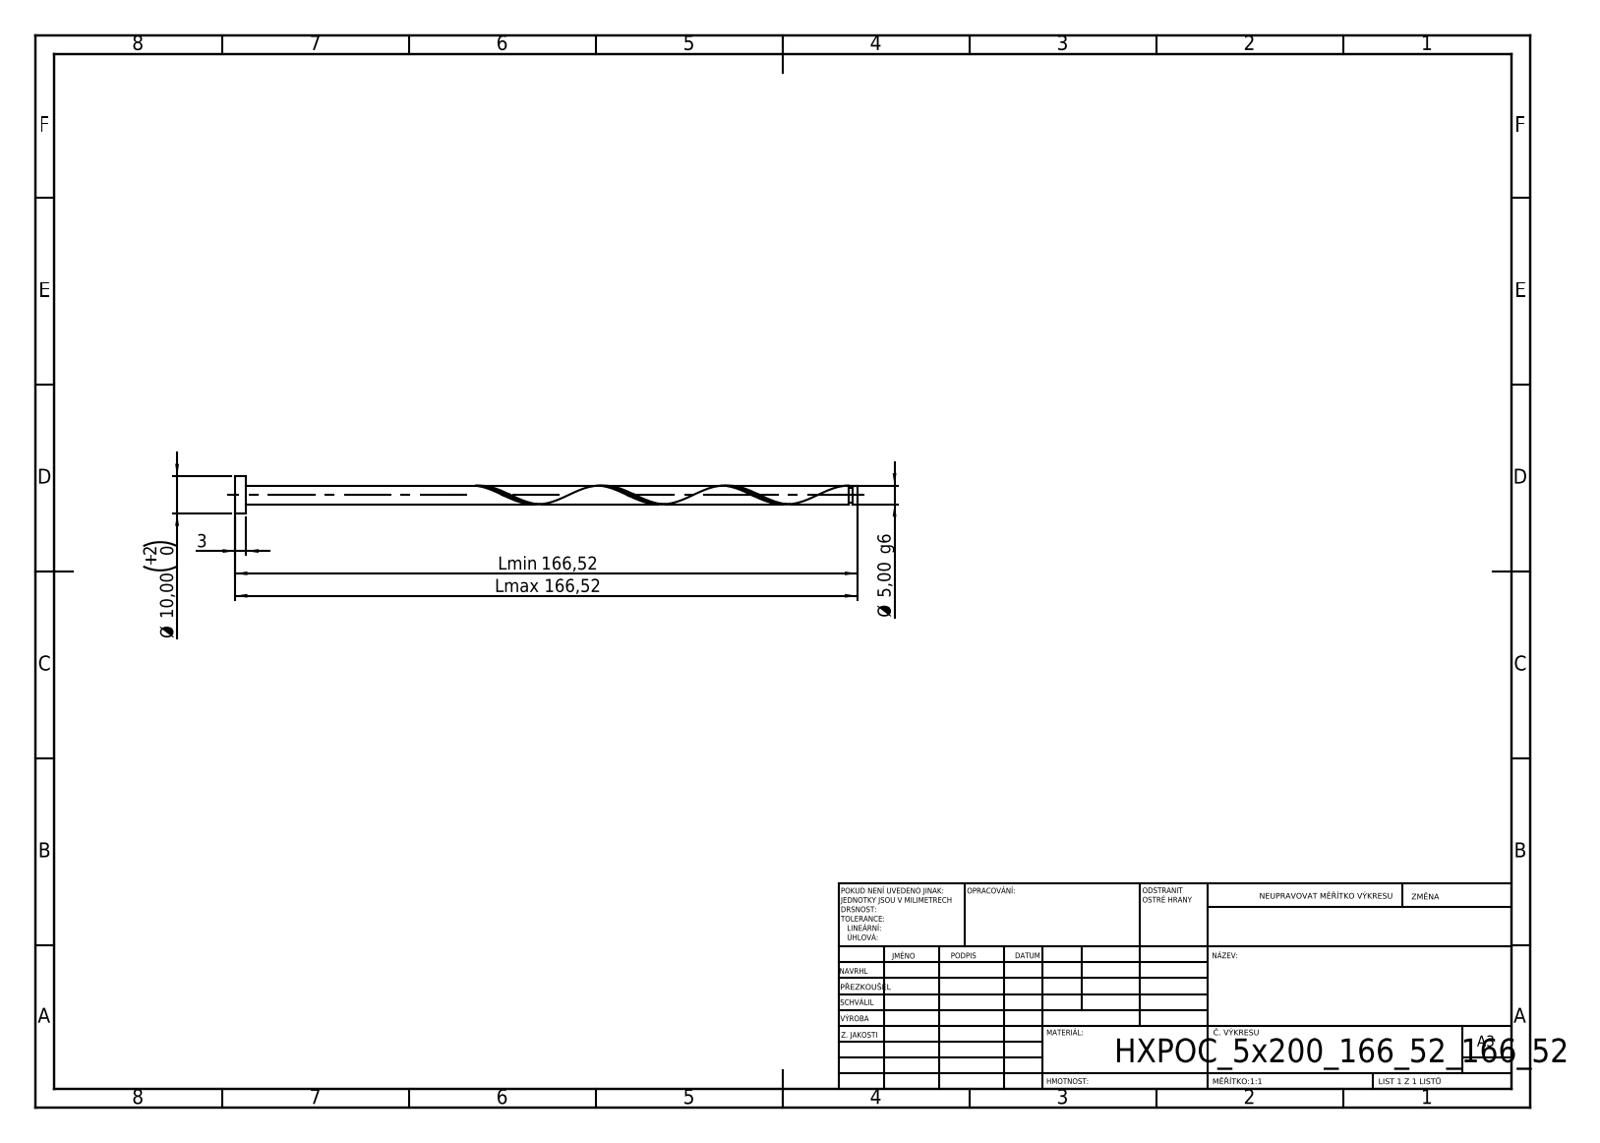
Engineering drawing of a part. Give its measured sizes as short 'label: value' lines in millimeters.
written by: SolidWorks 2019 (CONFIG_CONTROL_DESIGN)
unit: mm
bodies: 1 solid, 21 faces (6 planar, 14 cylindrical, 1 other)
size: 166.52 × 10 × 10
volume: 3 402 mm³; area: 2 885 mm²
bosses: 1× ⌀10, 1× ⌀5, 1× ⌀4
face distances: 3, 166.52, 163.52, 165.33, 162.33, 1.19, 164.33, 161.33, 1, 2.19
